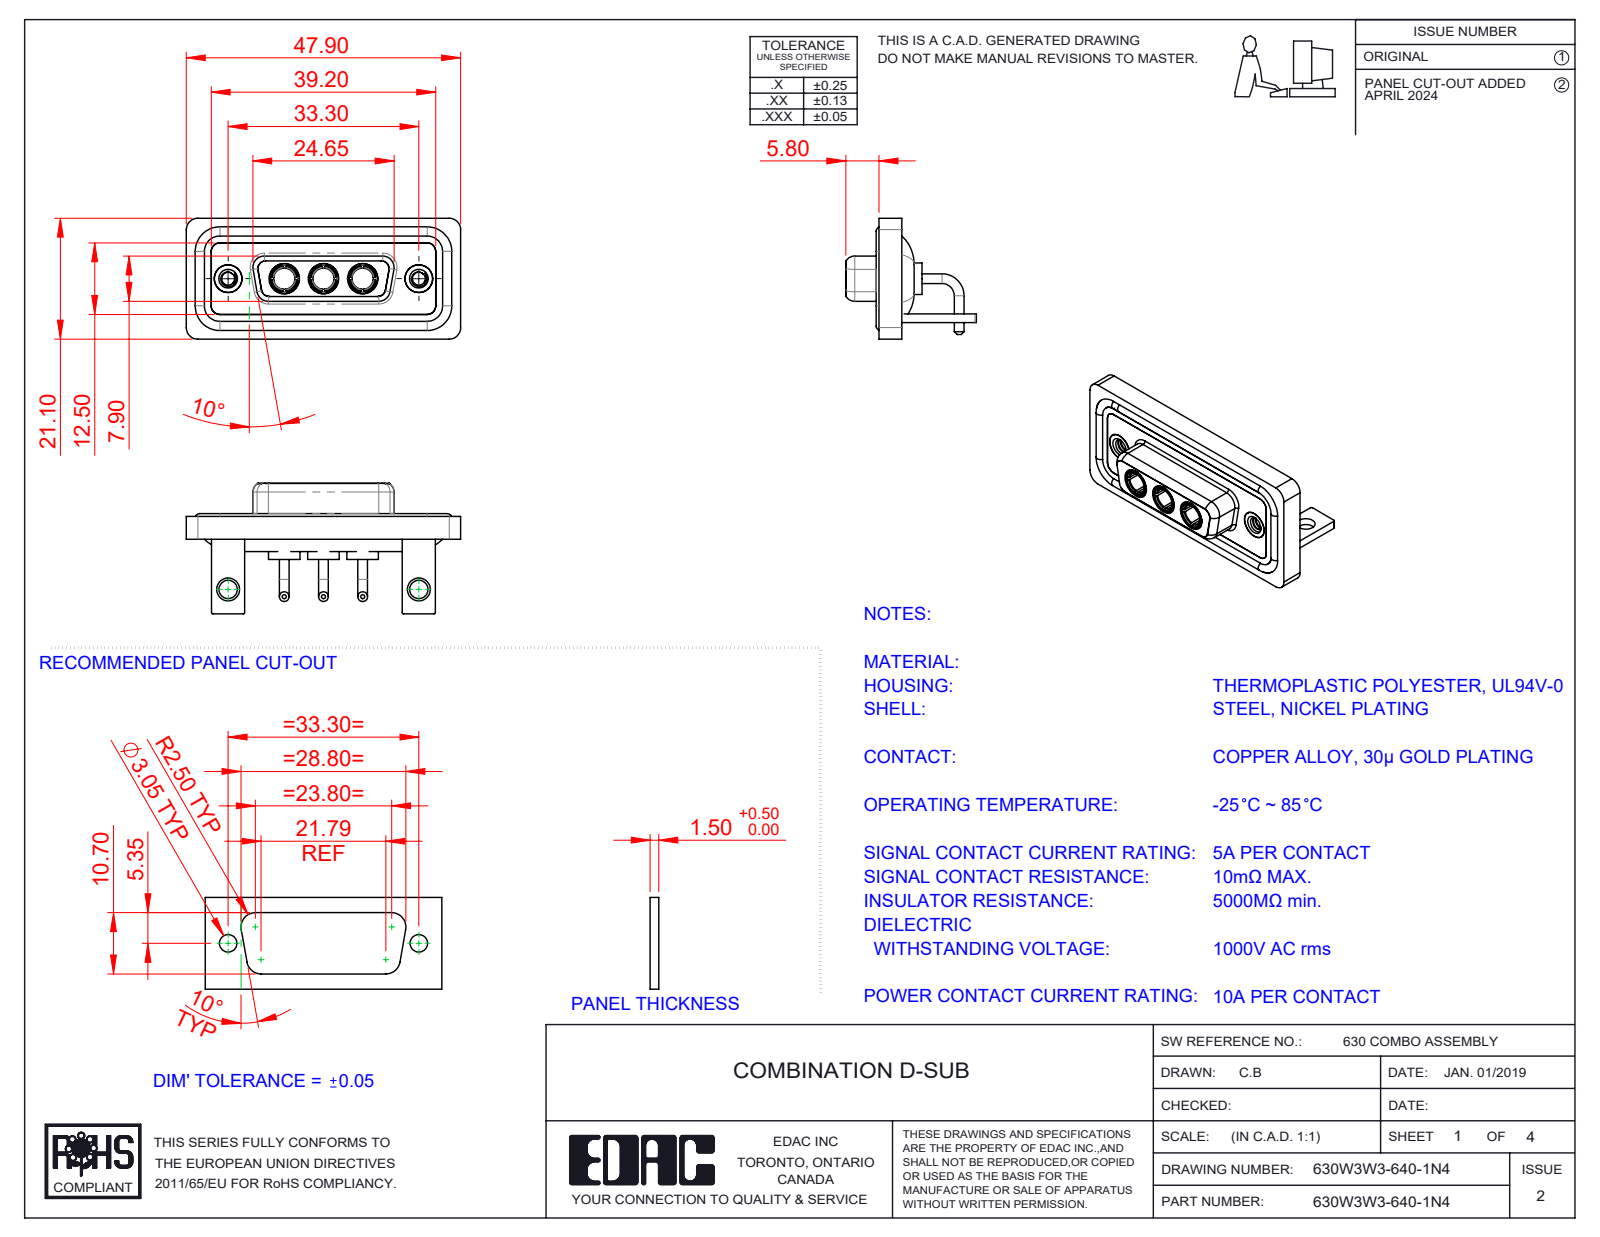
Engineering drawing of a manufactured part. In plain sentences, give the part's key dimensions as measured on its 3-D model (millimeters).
The part is named "630Combo Housing_3W3; 630Combo Shell Front_15 Contacts; 630Combo Threaded Rivet_2; Power Socket_10A RA (+4 more)". Its 3-D file was written by "SolidWorks 2023 (CONFIG_CONTROL_DESIGN)". It is 15 solids with 668 faces: 212 planar, 287 cylindrical and 169 other. Overall it measures 47.9 by 22.8 by 21.1 millimeters. Its volume is 6 373 cubic millimeters and its surface area 10 555 square millimeters. Round holes: 5 of diameter 4.85, 3 of diameter 3.7, 3 of diameter 5.3, 2 of diameter 2.26, 2 of diameter 3.2, 2 of diameter 4, 2 of diameter 4.05, 2 of diameter 5. Round bosses or shafts: 6 of diameter 1.7, 4 of diameter 1.6, 3 of diameter 5.5, 3 of diameter 5.2, 3 of diameter 4.96, 3 of diameter 4.75, 3 of diameter 3.75, 2 of diameter 4.95. Partial cylindrical surfaces (rounded edges, fillets, slot ends): 21 of radius 2, 18 of radius 1.5, 16 of radius 0.25, 12 of radius 1.35, 8 of radius 1.6, 5 of radius 0.5, 4 of radius 0.6, 4 of radius 0.65. The main face-to-face distances are 0.4, 2.9, 1.5, 1.8, 3.7, 1.1, 4.1, 1.6, 2.5, 1.4. The hole center spacings are 6.85, 9.8, 16.65, 23.5, 33.3, 13.7.
